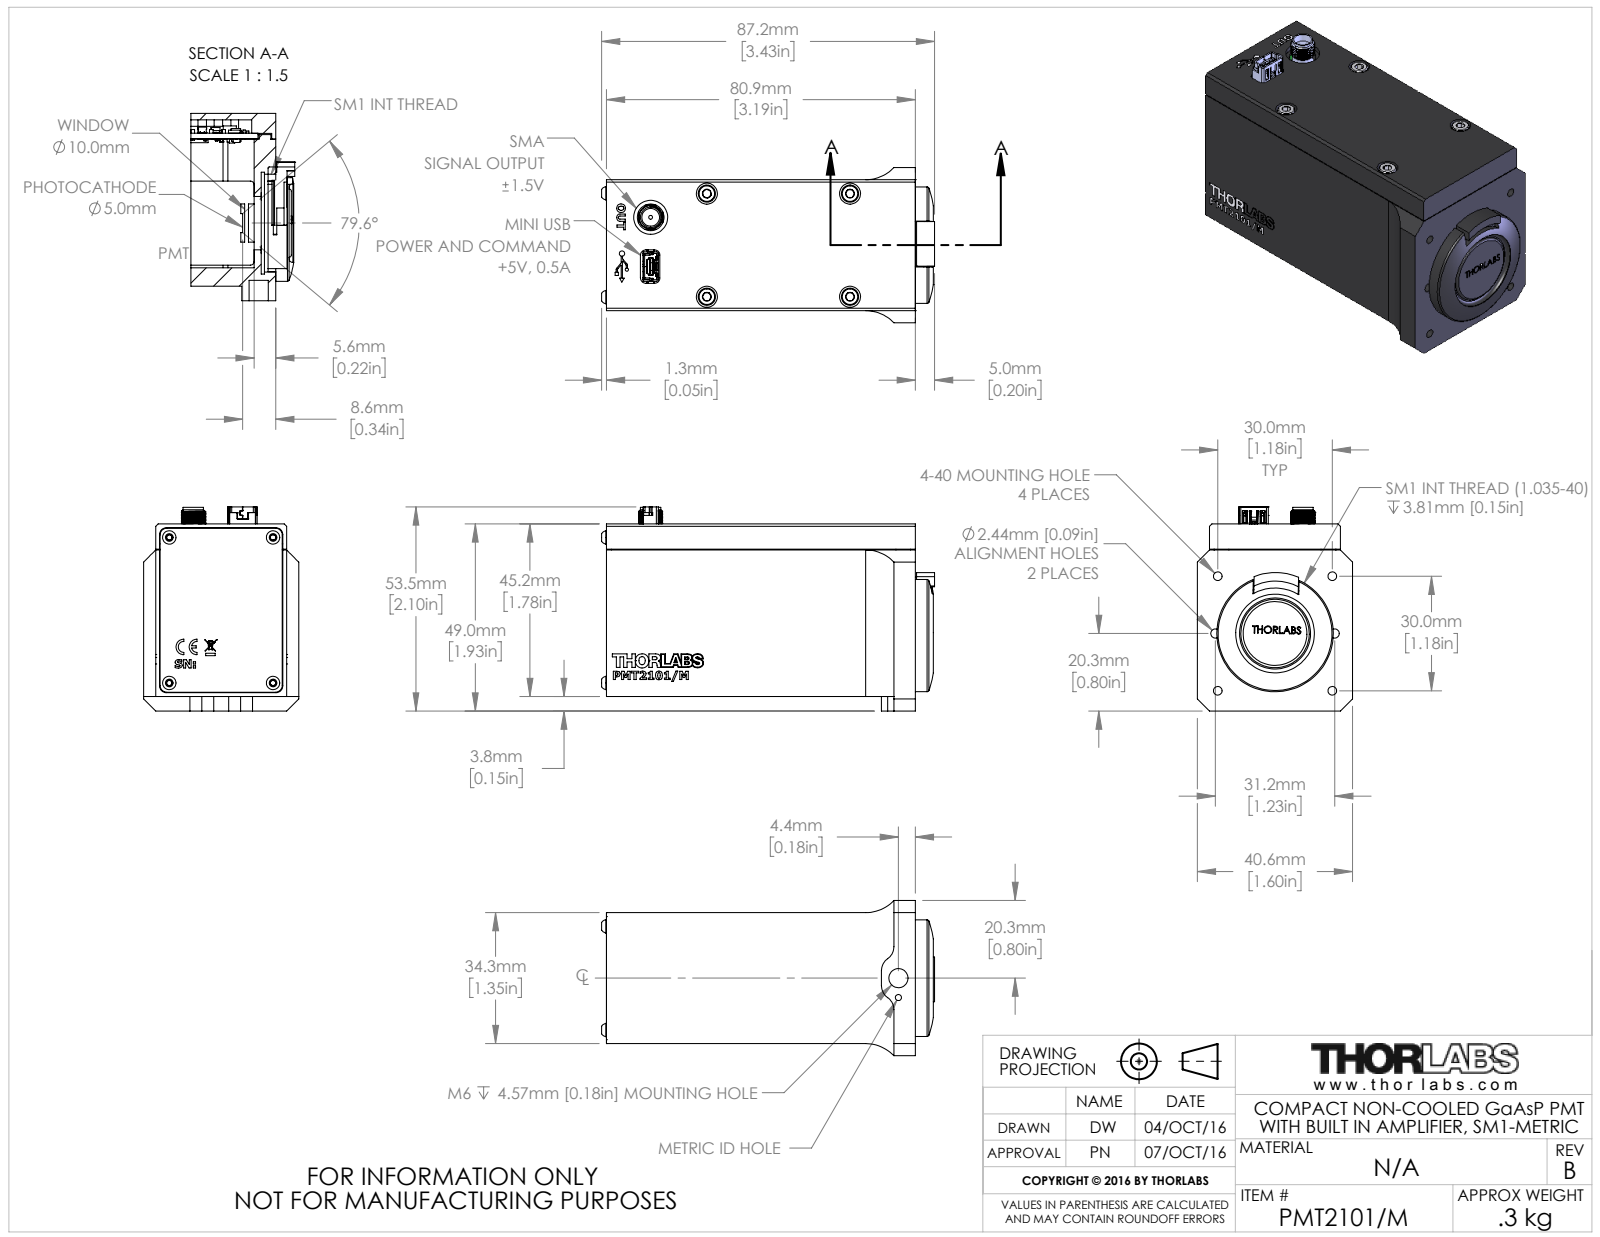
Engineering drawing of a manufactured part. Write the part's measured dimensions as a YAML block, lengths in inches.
part_name: "TTN092711-E0W"
step_written_by: "SolidWorks 2016 (AUTOMOTIVE_DESIGN)"
units: inches
bodies: {solids: 0, faces: 7339, planar: 4041, cylindrical: 2315, other: 983}
overall_size: [3.433, 2.105, 1.6]
round_holes:
  - {diameter: 0.063, count: 10}
  - {diameter: 0.094, count: 8}
  - {diameter: 0.024, count: 5}
  - {diameter: 0.067, count: 5}
  - {diameter: 0.114, count: 5}
  - {diameter: 0.081, count: 4}
  - {diameter: 0.089, count: 4}
  - {diameter: 0.173, count: 4}
  - {diameter: 0.217, count: 4}
  - {diameter: 0.197, count: 3}
  - {diameter: 0.016, count: 2}
  - {diameter: 0.035, count: 2}
round_bosses_or_shafts:
  - {diameter: 0.138, count: 9}
  - {diameter: 0.079, count: 8}
  - {diameter: 0.058, count: 8}
  - {diameter: 0.02, count: 8}
  - {diameter: 0.177, count: 4}
  - {diameter: 0.098, count: 4}
  - {diameter: 0.075, count: 4}
  - {diameter: 0.047, count: 4}
partial_cylinders:
  - {radius: 0.004, count: 87}
  - {radius: 0.008, count: 34}
  - {radius: 0.02, count: 24}
  - {radius: 0.07, count: 20}
  - {radius: 0.135, count: 20}
  - {radius: 0.015, count: 10}
  - {radius: 0.15, count: 8}
  - {radius: 0.01, count: 6}
face_to_face_distances: [0.215, 1.135, 1.35, 0.893, 0.027, 0.866, 1.78, 0.058, 0.92, 1.577]
hole_center_spacings: [0.922, 0.145, 0.513, 0.551, 0.063, 0.078, 0.205, 0.39]
